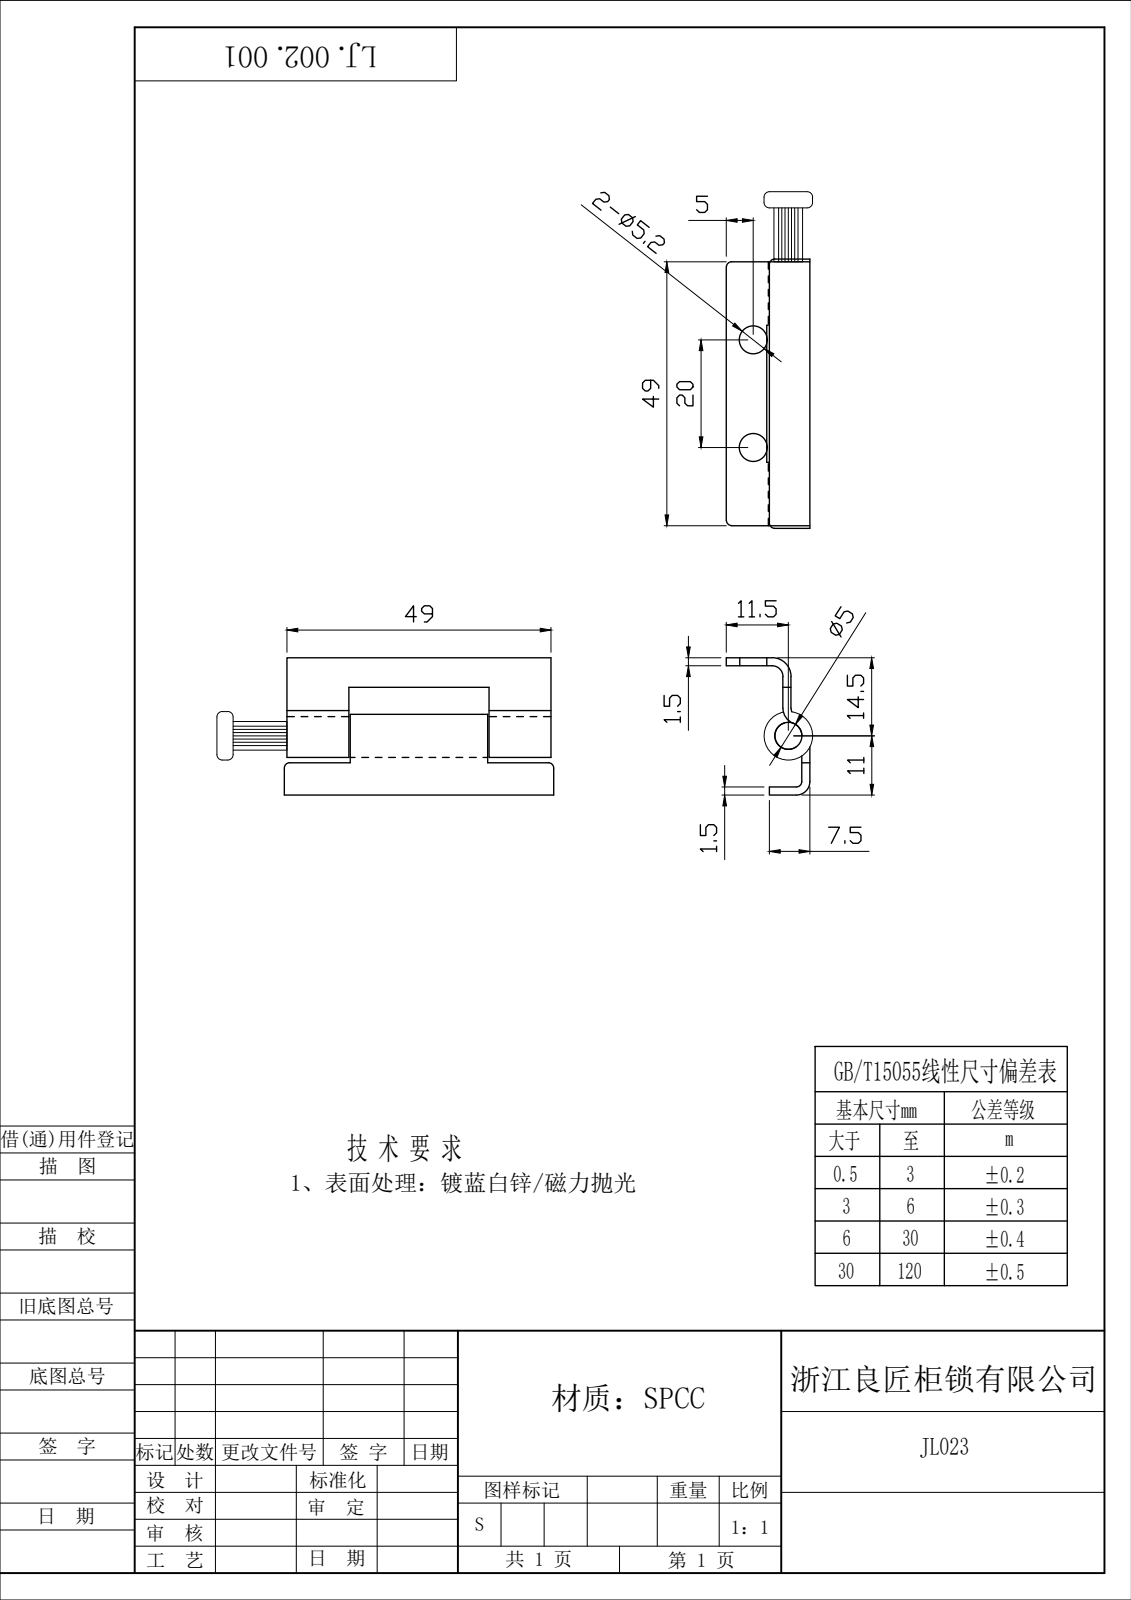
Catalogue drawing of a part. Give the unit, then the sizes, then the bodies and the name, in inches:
Units: inches
Overall size (bounding box): 2.441 × 1.004 × 0.63
Round holes (diameter × count): ⌀0.205 ×2, ⌀0.197 ×1, ⌀0.197 ×1
Round bosses / shafts (diameter × count): ⌀0.354 ×1, ⌀0.209 ×1
Partial cylindrical surfaces — rounded edges, fillets, slot ends (radius × count): R0.01 ×9, R0.039 ×6, R0.059 ×1, R0.079 ×1, R0.098 ×1, R0.118 ×1, R0.138 ×1
Main face-to-face distances: 0.059, 0.945, 0.138, 1.004, 0.886, 0.197, 0.079, 0.413, 0.354, 0.157
Hole centre spacings: 0.787
Volume: 0.341 in³ · Surface area: 10.52 in²
Bodies: 3 solids, 88 faces (28 planar, 37 cylindrical, 23 other)
STEP written by: Rhino 8.5 (CONFIG_CONTROL_DESIGN)
